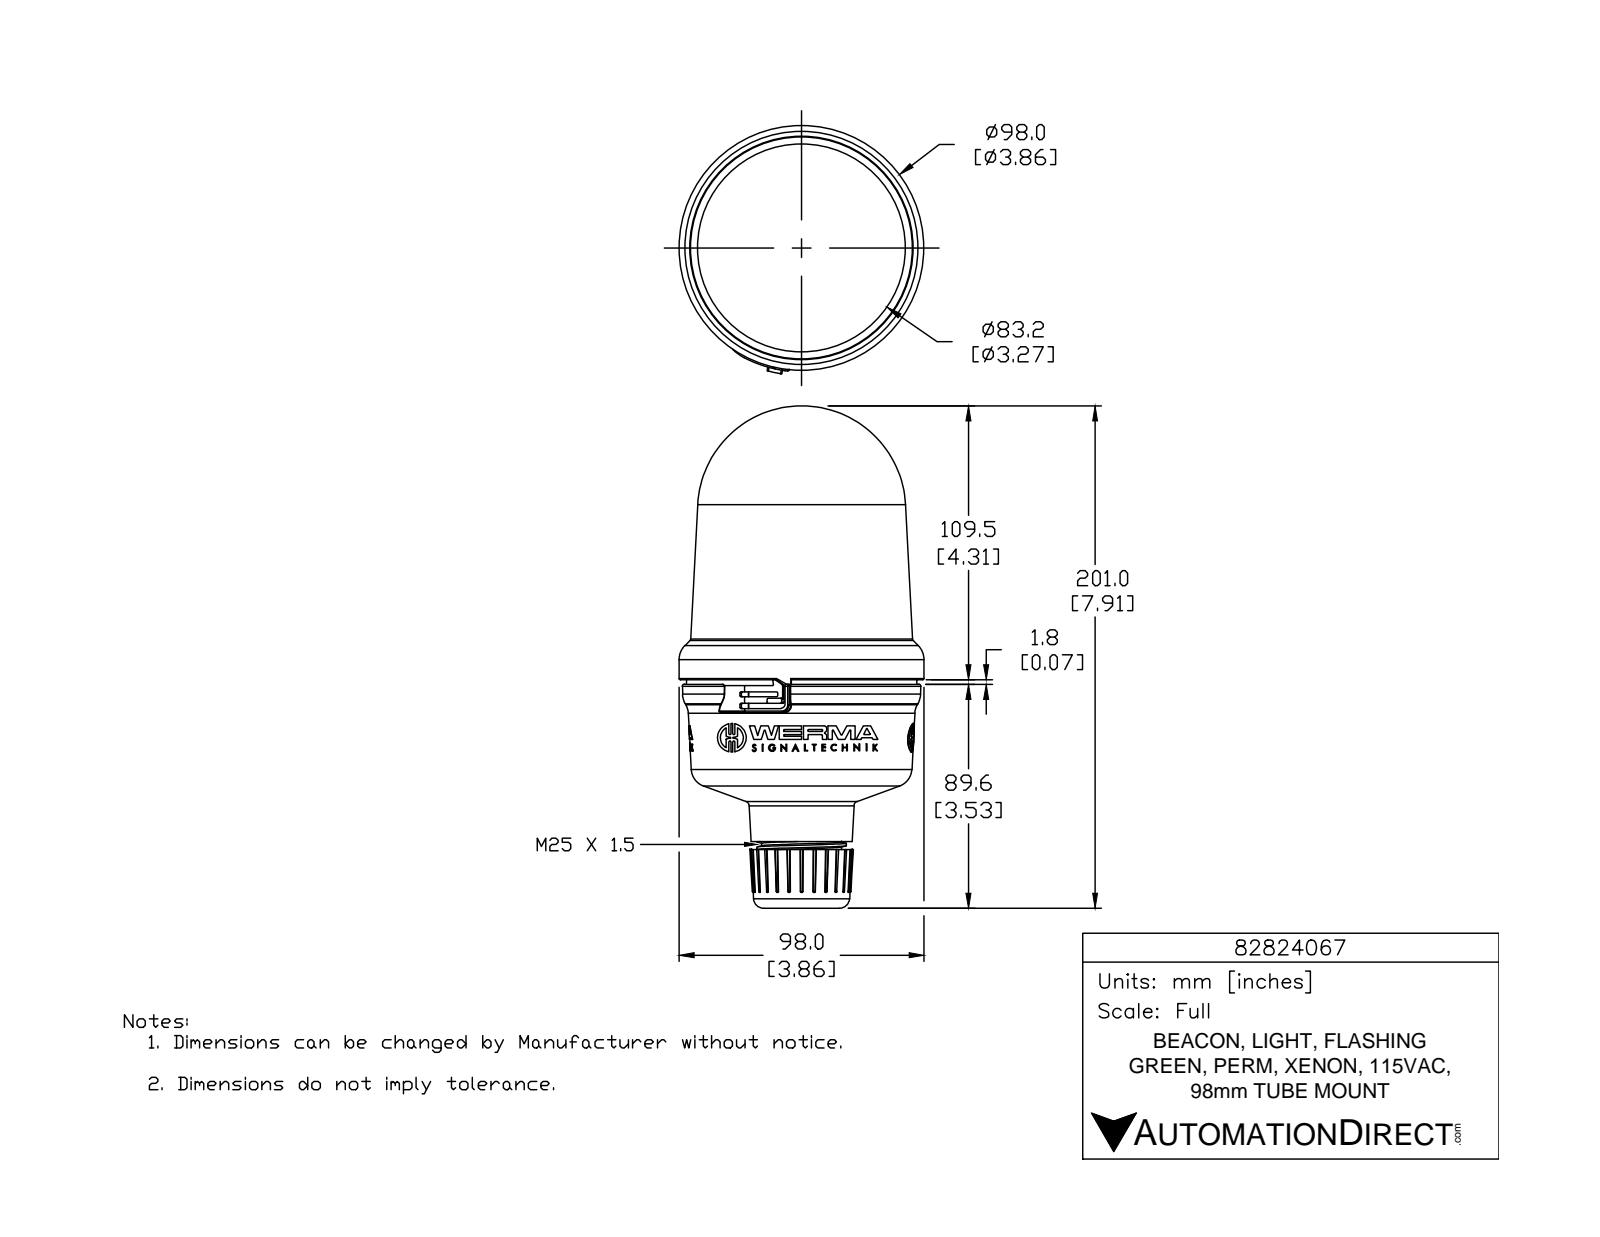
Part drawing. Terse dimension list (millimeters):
name: 82824067
written by: SolidWorks 2015 (AUTOMOTIVE_DESIGN)
unit: mm
bodies: 1 solid, 1006 faces (554 planar, 189 cylindrical, 263 other)
size: 201 × 99.4 × 98
volume: 896 400 mm³; area: 58 960 mm²
holes: 3× ⌀2, 1× ⌀25.7, 1× ⌀26
bosses: 3× ⌀11.5, 3× ⌀2.9, 1× ⌀98, 1× ⌀35.8, 1× ⌀32
rounds: 12× R0.5, 9× R0.2, 6× R0.2, 6× R0.4, 6× R0.4, 6× R0.4, 6× R6.7, 3× R0.2
face distances: 56.2, 11.7, 68, 8.5, 3.2, 64.7, 66.1, 62.9, 54.4, 1.9
